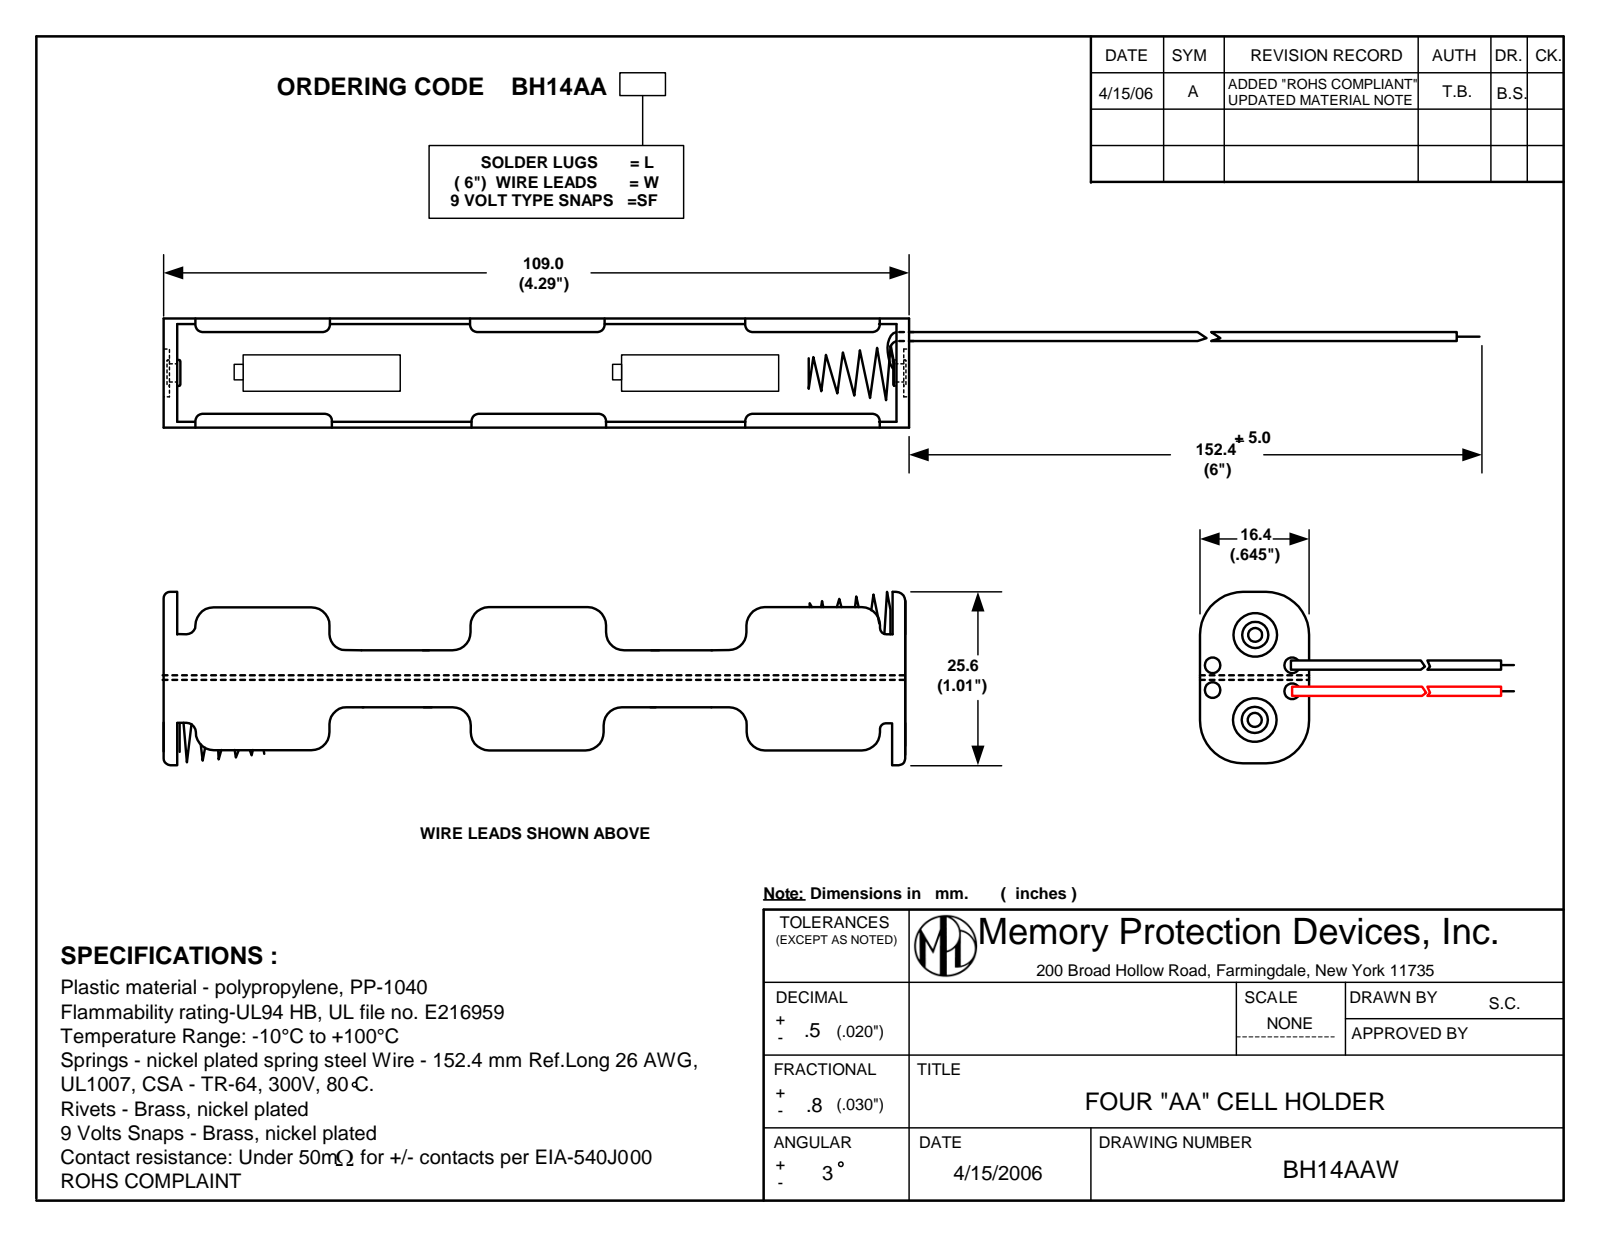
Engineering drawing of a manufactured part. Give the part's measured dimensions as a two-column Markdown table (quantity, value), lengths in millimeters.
| quantity | value |
| --- | --- |
| part name | BH14AAW |
| STEP written by | SolidWorks 2017 (AUTOMOTIVE_DESIGN) |
| units | millimeters |
| bodies | 9 solids, 621 faces (147 planar, 262 cylindrical, 212 other) |
| overall size | 264 × 25.6 × 16.4 |
| volume | 8 227 mm³ |
| surface area | 15 597 mm² |
| round holes (diameter × count) | 0.4 × 2, 1.27 × 2, 2.3 × 2, 2.54 × 2, 3 × 2, 9.5 × 2 |
| round bosses / shafts (diameter × count) | 7 × 2, 6.35 × 2, 6.2 × 2, 0.81 × 2, 0.63 × 1 |
| partial cylindrical surfaces (radius × count) | 0.2 × 32, 2.54 × 24, 1.27 × 16, 0.75 × 8, 4 × 4, 5.54 × 4, 9.78 × 4, 0.32 × 1 |
| main face-to-face distances | 1.3, 15.1, 16.4, 13.8, 107.7, 106.4, 0.31, 108.69, 0.99, 107.39 |
| hole center spacings | 7.23, 10.09, 3.84, 12.9 |
